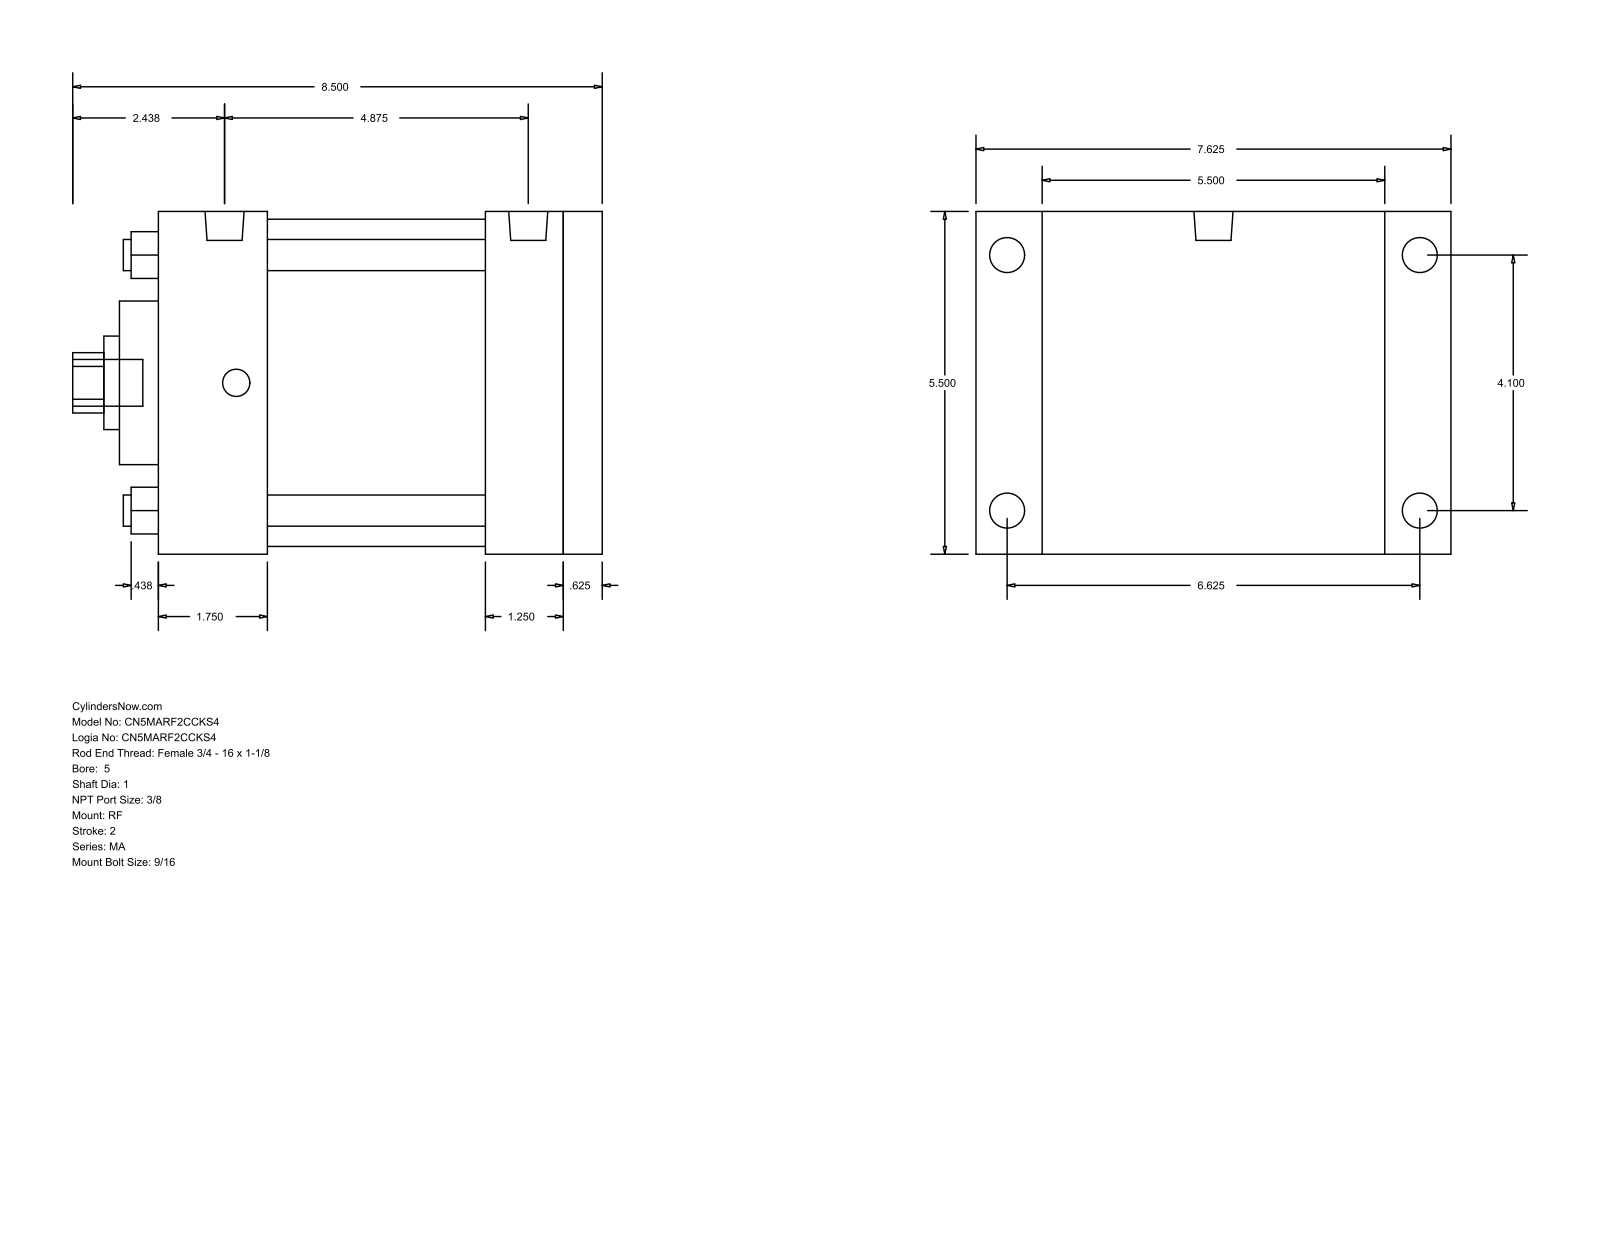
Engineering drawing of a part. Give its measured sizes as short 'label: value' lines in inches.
name: MA_RF__0500_1
written by: GSSL Pune (CONFIG_CONTROL_DESIGN)
unit: in
bodies: 0 solids, 94 faces (65 planar, 29 cylindrical, 0 other)
size: 8.5 × 7.625 × 5.5
holes: 4× ⌀0.5, 1× ⌀1, 1× ⌀1.5, 1× ⌀2.625, 1× ⌀5.25
bosses: 4× ⌀0.563, 4× ⌀0.437, 2× ⌀0.627, 1× ⌀0.75
rounds: 1× R0.484
face distances: 5.5, 7.125, 0.625, 6.5, 1.75, 4.75, 5.375, 5.25, 3.5, 1.25
hole spacings: 2.899, 4.1, 5.798
